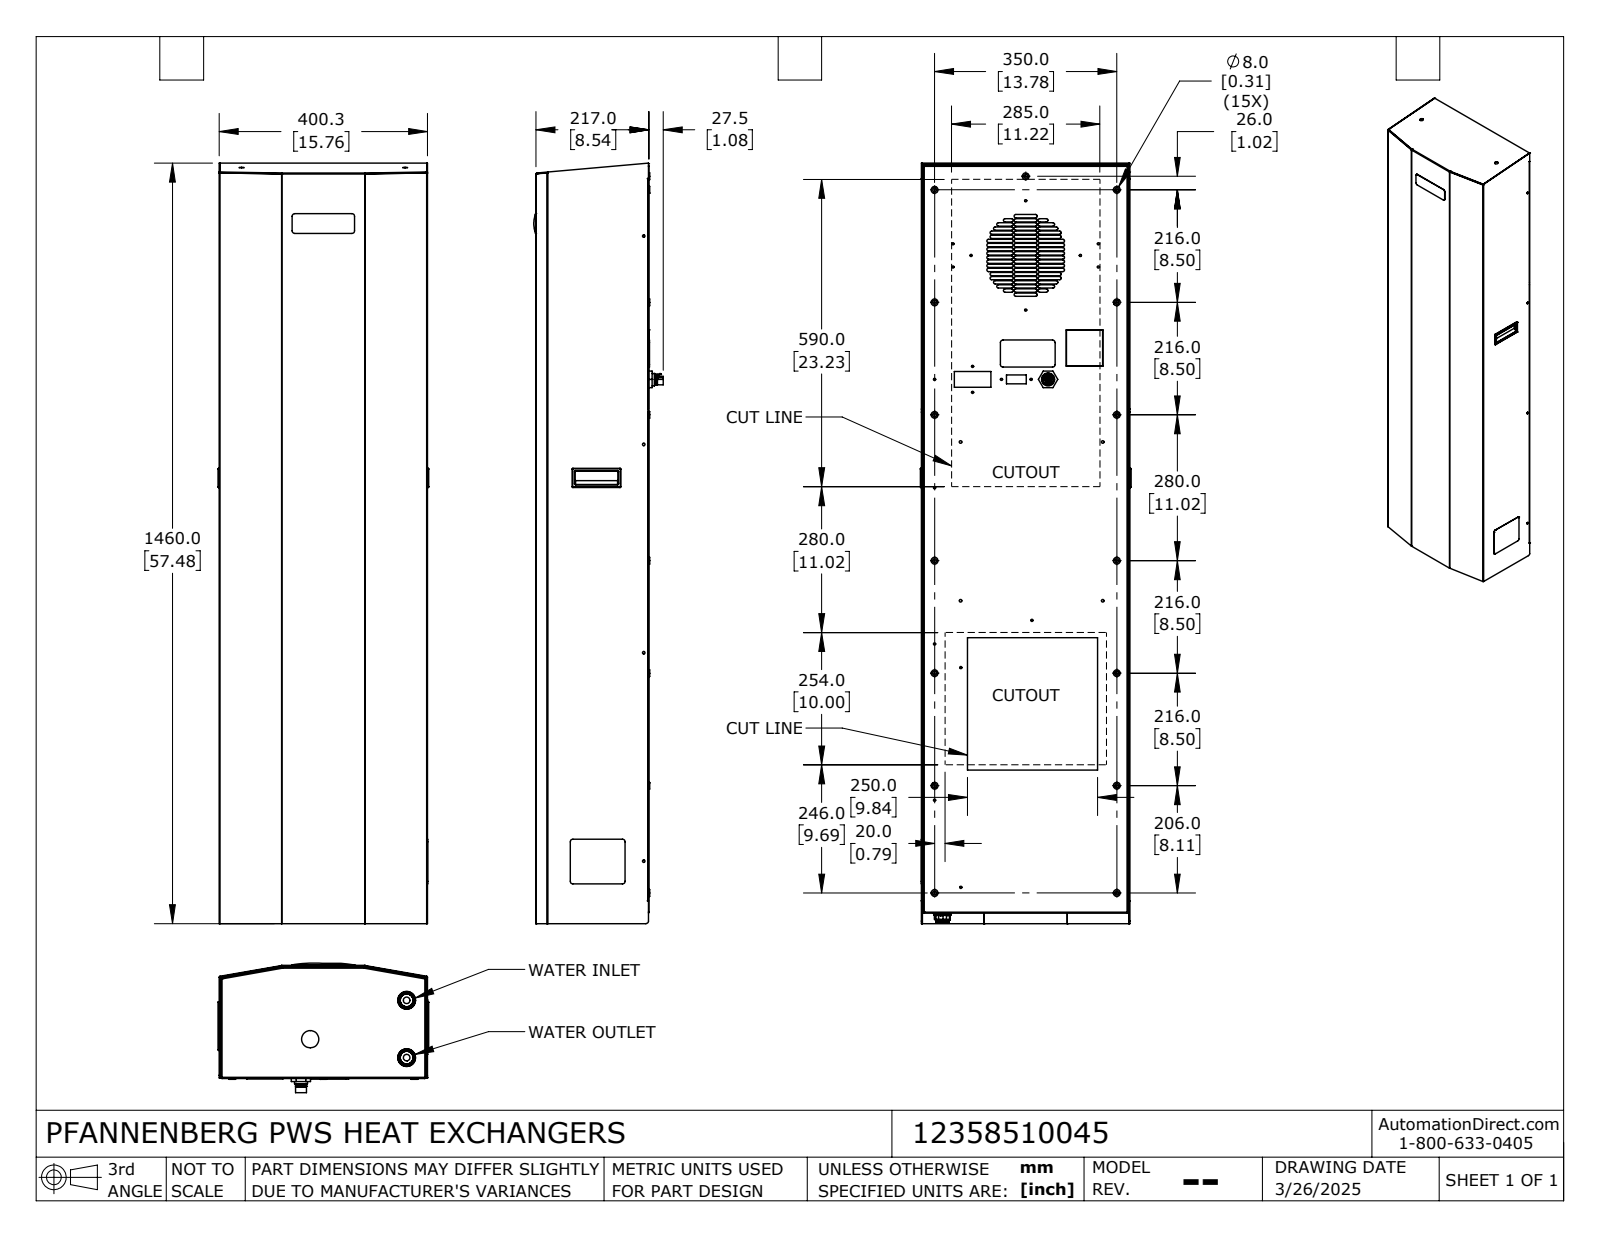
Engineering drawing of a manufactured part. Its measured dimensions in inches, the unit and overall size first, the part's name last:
Units: inches
Overall size (bounding box): 57.48 × 15.917 × 9.797
Round holes (diameter × count): ⌀0.165 ×19, ⌀0.283 ×15, ⌀0.169 ×5, ⌀0.209 ×5, ⌀0.189 ×4, ⌀0.197 ×4, ⌀0.472 ×4, ⌀0.394 ×2, ⌀0.5 ×2, ⌀0.591 ×2, ⌀0.992 ×2, ⌀1 ×2
Round bosses / shafts (diameter × count): ⌀0.512 ×15, ⌀0.079 ×4, ⌀0.984 ×2, ⌀0.965 ×2, ⌀0.571 ×2, ⌀1.102 ×1, ⌀0.906 ×1
Partial cylindrical surfaces — rounded edges, fillets, slot ends (radius × count): R0.125 ×112, R0.039 ×52, R0.031 ×20, R0.198 ×15, R0.197 ×13, R0.087 ×11, R0.076 ×7, R0.047 ×4
Main face-to-face distances: 0.045, 0.056, 0.031, 0.087, 0.166, 15.504, 0.045, 15.714, 15.715, 15.669
Hole centre spacings: 0.294, 5.846, 6.393, 7.439, 9.674, 0.244, 15.748, 0.231
Volume: 7 059 in³ · Surface area: 8 432 in²
Bodies: 12 solids, 1584 faces (809 planar, 660 cylindrical, 115 other)
Part name (STEP PRODUCT): 12358510045_Default
STEP written by: SolidWorks 2024 (CONFIG_CONTROL_DESIGN)
